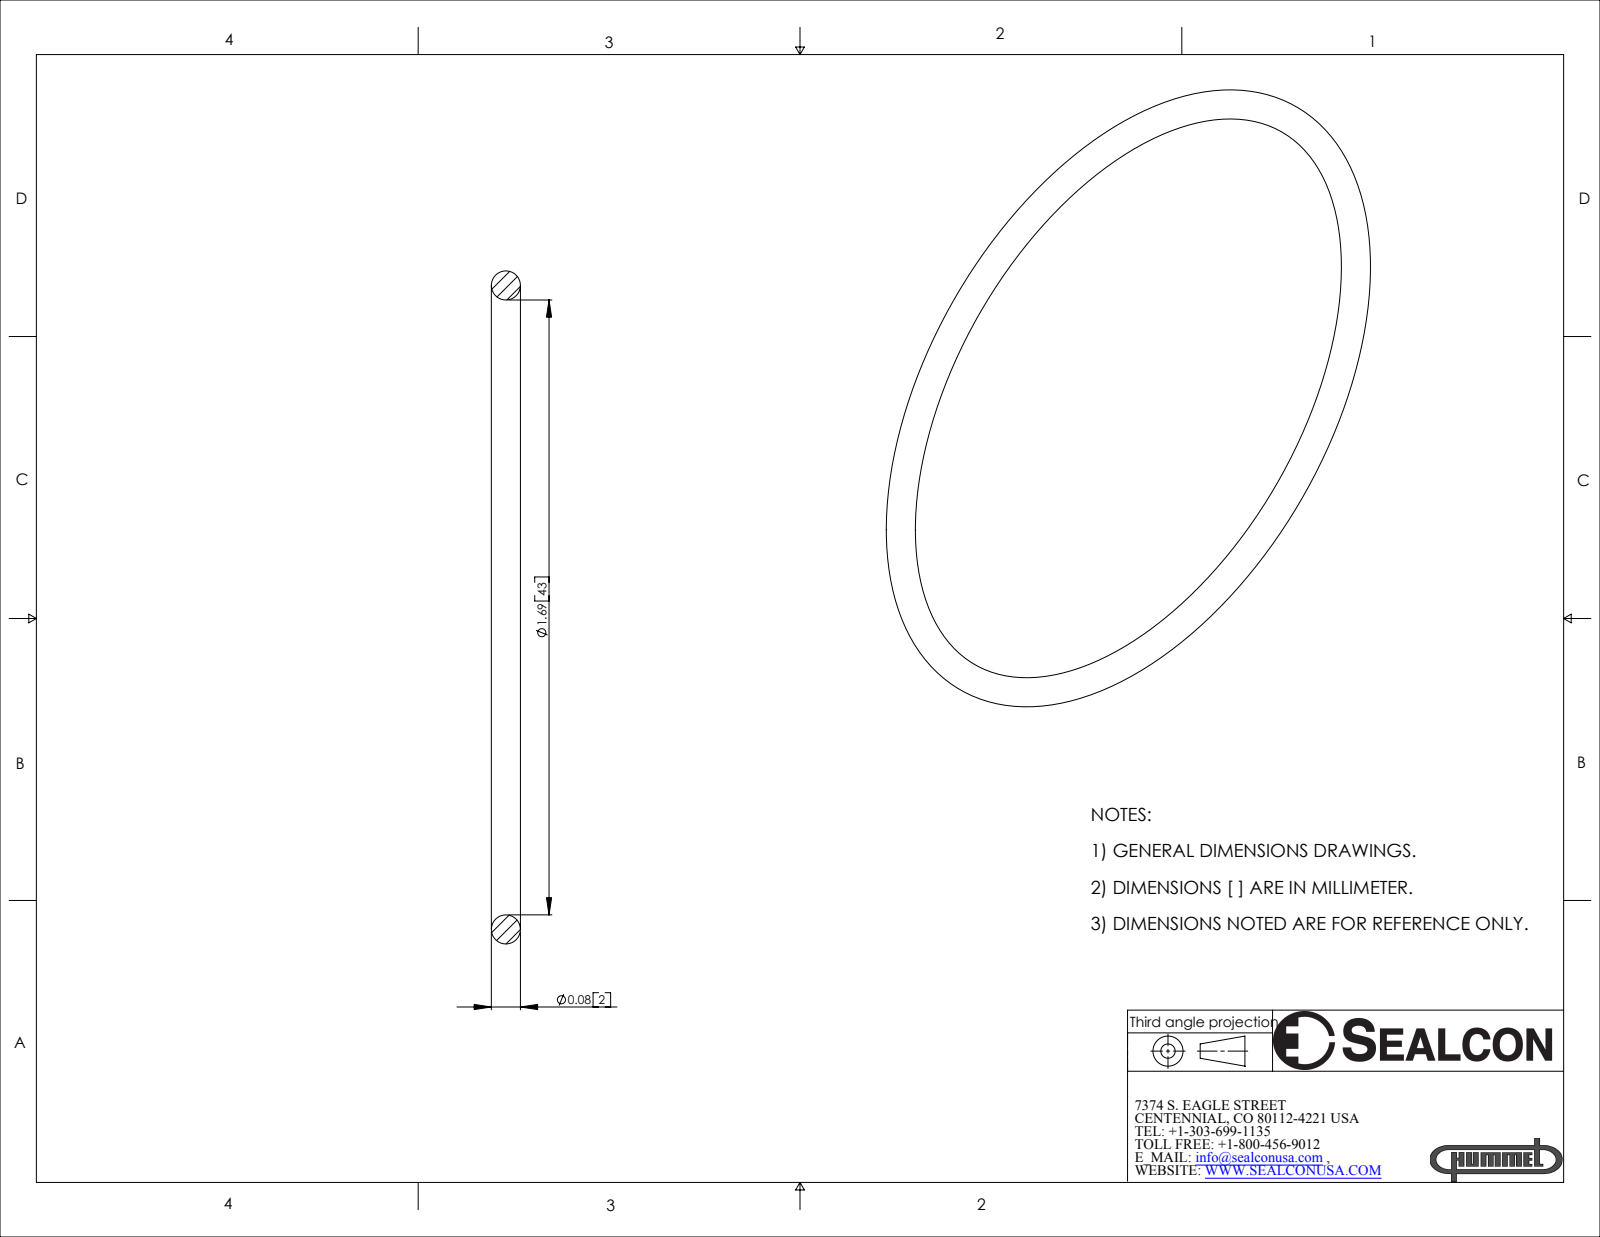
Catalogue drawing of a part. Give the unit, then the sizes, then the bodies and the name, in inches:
Units: inches
Overall size (bounding box): 1.85 × 1.85 × 0.08
Volume: 0.028 in³ · Surface area: 1.398 in²
Bodies: 1 solid, 4 faces (0 planar, 0 cylindrical, 4 other)
Part name (STEP PRODUCT): OM-50-BN
STEP written by: SolidWorks 2007 (CONFIG_CONTROL_DESIGN)
